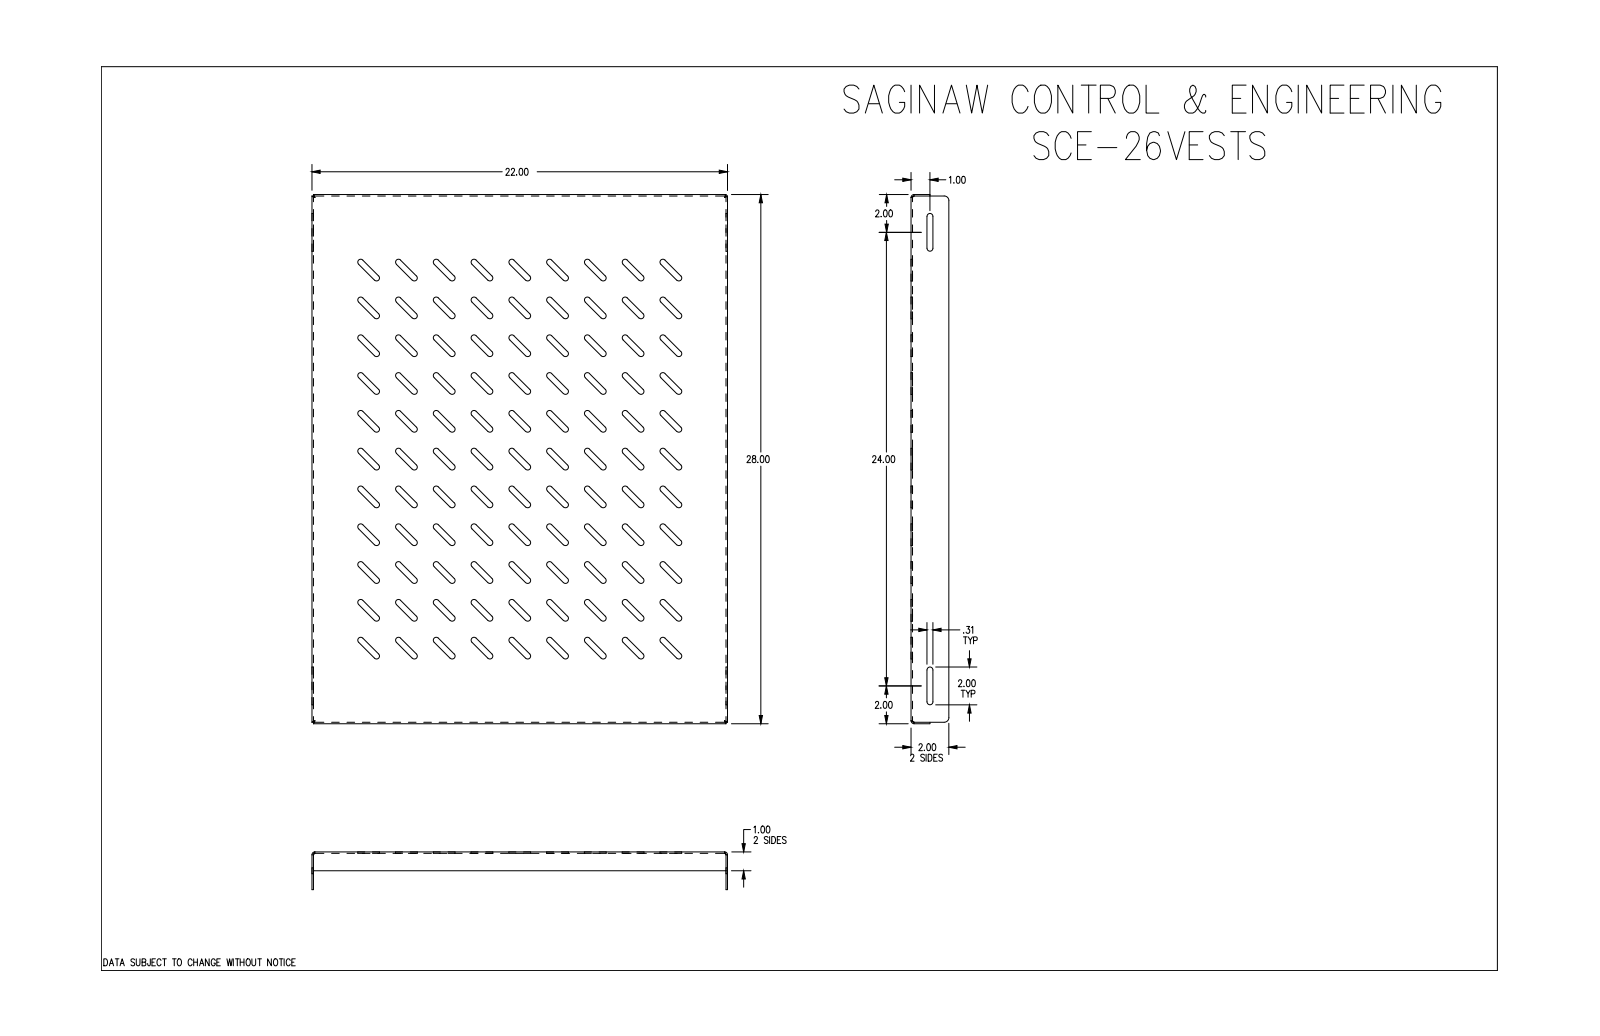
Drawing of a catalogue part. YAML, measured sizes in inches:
part_name: "SCE-26VESTS"
step_written_by: "SolidWorks 2019 (CONFIG_CONTROL_DESIGN)"
units: inches
bodies: {solids: 1, faces: 458, planar: 228, cylindrical: 222, other: 8}
overall_size: [28, 22, 2]
volume: 55.49
surface_area: 1459
partial_cylinders:
  - {radius: 0.156, count: 202}
  - {radius: 0.078, count: 4}
  - {radius: 0.156, count: 4}
  - {radius: 0.02, count: 2}
  - {radius: 0.25, count: 2}
face_to_face_distances: [0.078, 21.922, 21.844, 22, 27.922, 27.844, 28, 2.828, 1, 5.656]
